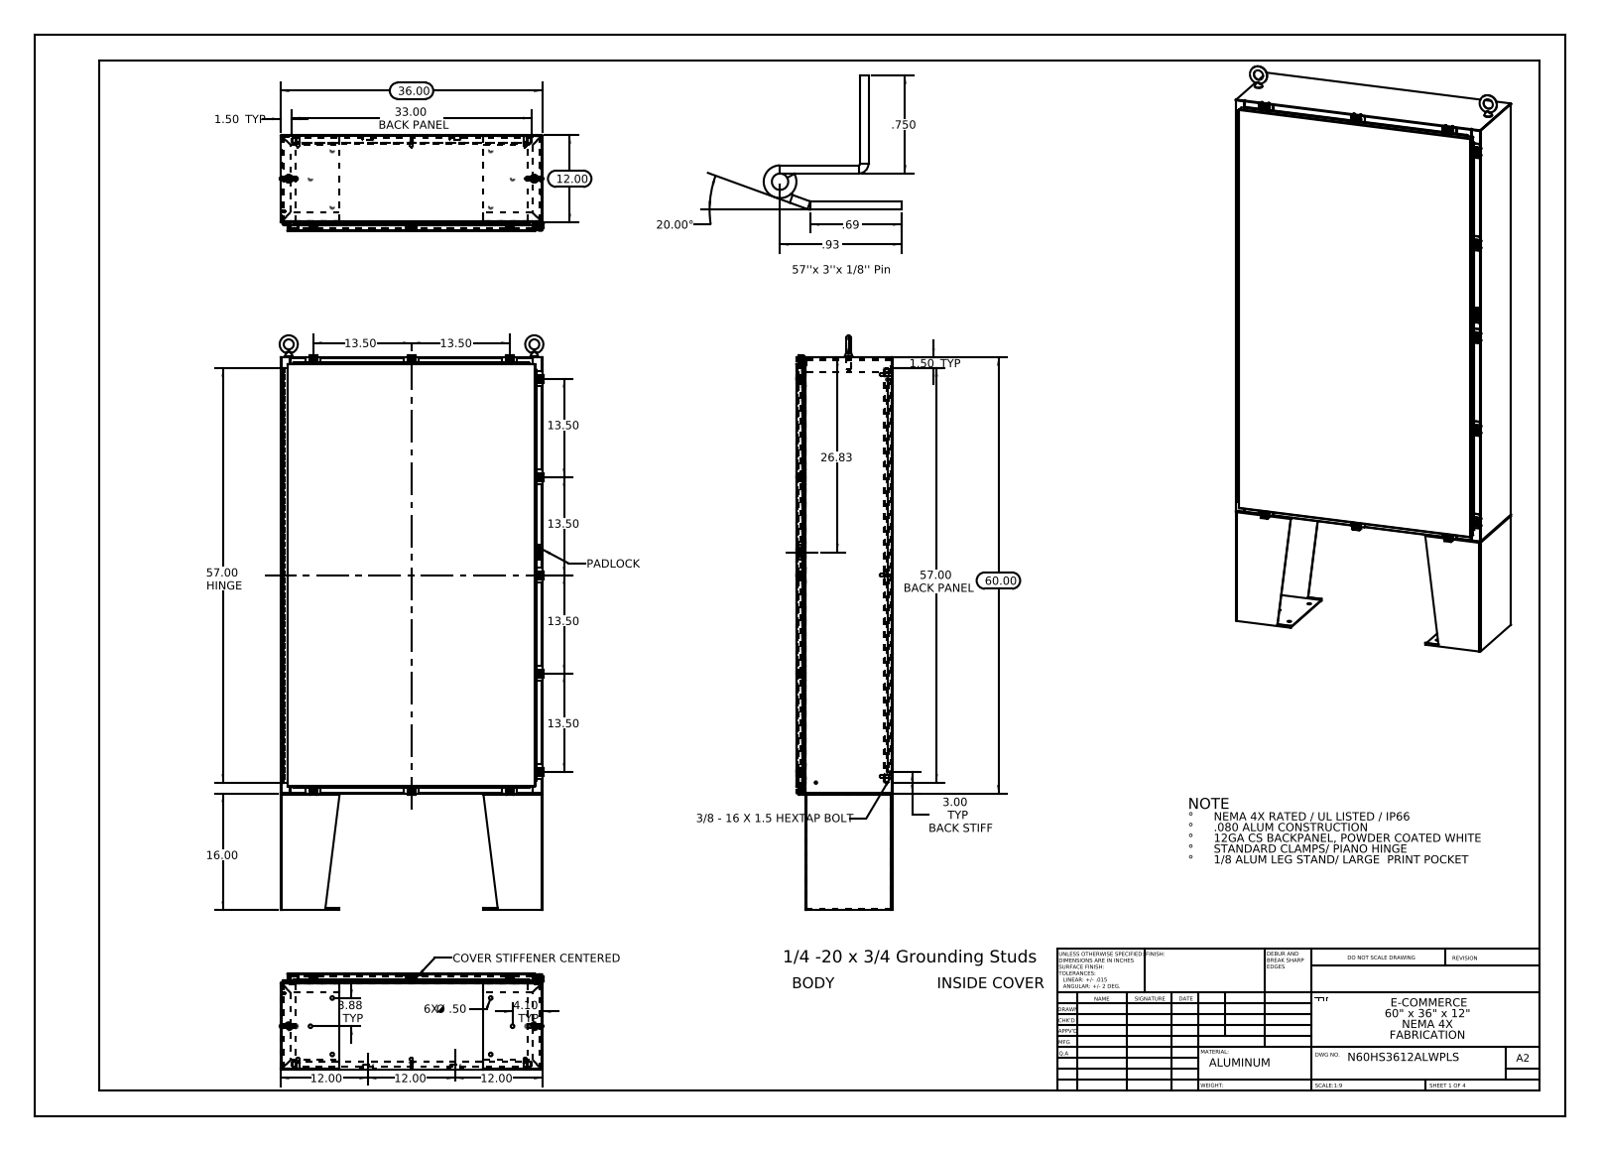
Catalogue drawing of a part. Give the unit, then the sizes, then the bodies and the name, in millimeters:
Units: millimetres
Overall size (bounding box): 2006.6 × 923.2 × 335.3
Round holes (diameter × count): ⌀12.7 ×14, ⌀5.4 ×11, ⌀6.6 ×11, ⌀6.4 ×8, ⌀19.1 ×4, ⌀3.2 ×2, ⌀3.2 ×1
Round bosses / shafts (diameter × count): ⌀6.4 ×12, ⌀12.7 ×11, ⌀10.1 ×11, ⌀15.9 ×10, ⌀9.5 ×8, ⌀8.4 ×8, ⌀4 ×8, ⌀3.6 ×8
Partial cylindrical surfaces — rounded edges, fillets, slot ends (radius × count): R1.5 ×50, R0.3 ×39, R2.2 ×33, R3 ×22, R3.6 ×22, R1.3 ×17, R2 ×16, R2.3 ×16
Main face-to-face distances: 1.9, 333.4, 2.6, 331.5, 27.3, 335.3, 308, 25.4, 306.1, 29.9
Hole centre spacings: 342.9, 347, 685.8, 56.5, 181.3, 637.4, 701.7, 757
Volume: 15 100 000 mm³ · Surface area: 14 330 000 mm²
Bodies: 93 solids, 3674 faces (1872 planar, 1518 cylindrical, 284 other)
Part name (STEP PRODUCT): N60HS3612SSWPLS Door Stiffener; N60HS3612SSWPLS Standard Clamps; N60HS3612SSWPLS Clamp Assembly; N60HS3612SSWPLS Hinge Cover Side (+8 more)
STEP written by: SolidWorks 2013 (CONFIG_CONTROL_DESIGN)
